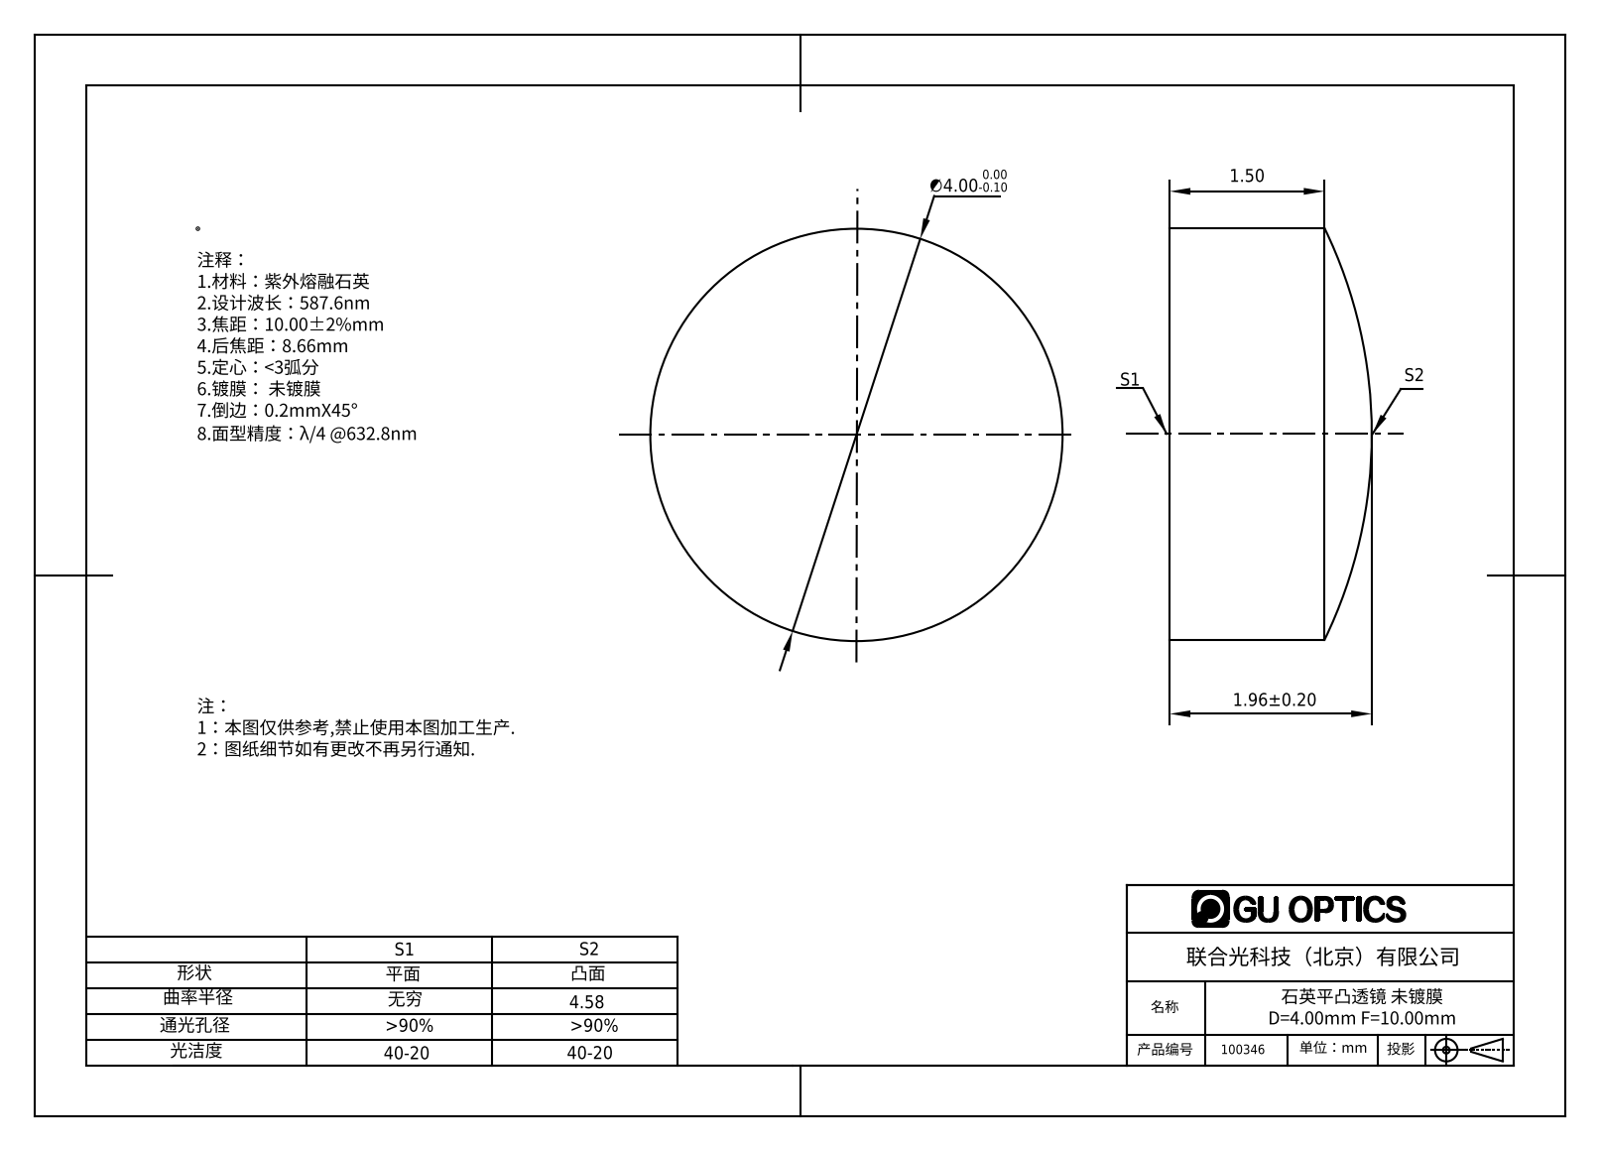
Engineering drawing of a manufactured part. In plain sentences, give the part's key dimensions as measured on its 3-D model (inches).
The part is named "100346". Its 3-D file was written by "SolidWorks 2016 (AUTOMOTIVE_DESIGN)". It is 1 solid with 5 faces: 1 planar, 2 cylindrical and 2 other. Overall it measures 0.157 by 0.157 by 0.077 inches. Its volume is 0.001 cubic inches and its surface area 0.07 square inches. Round bosses or shafts: 1 of diameter 0.157.
